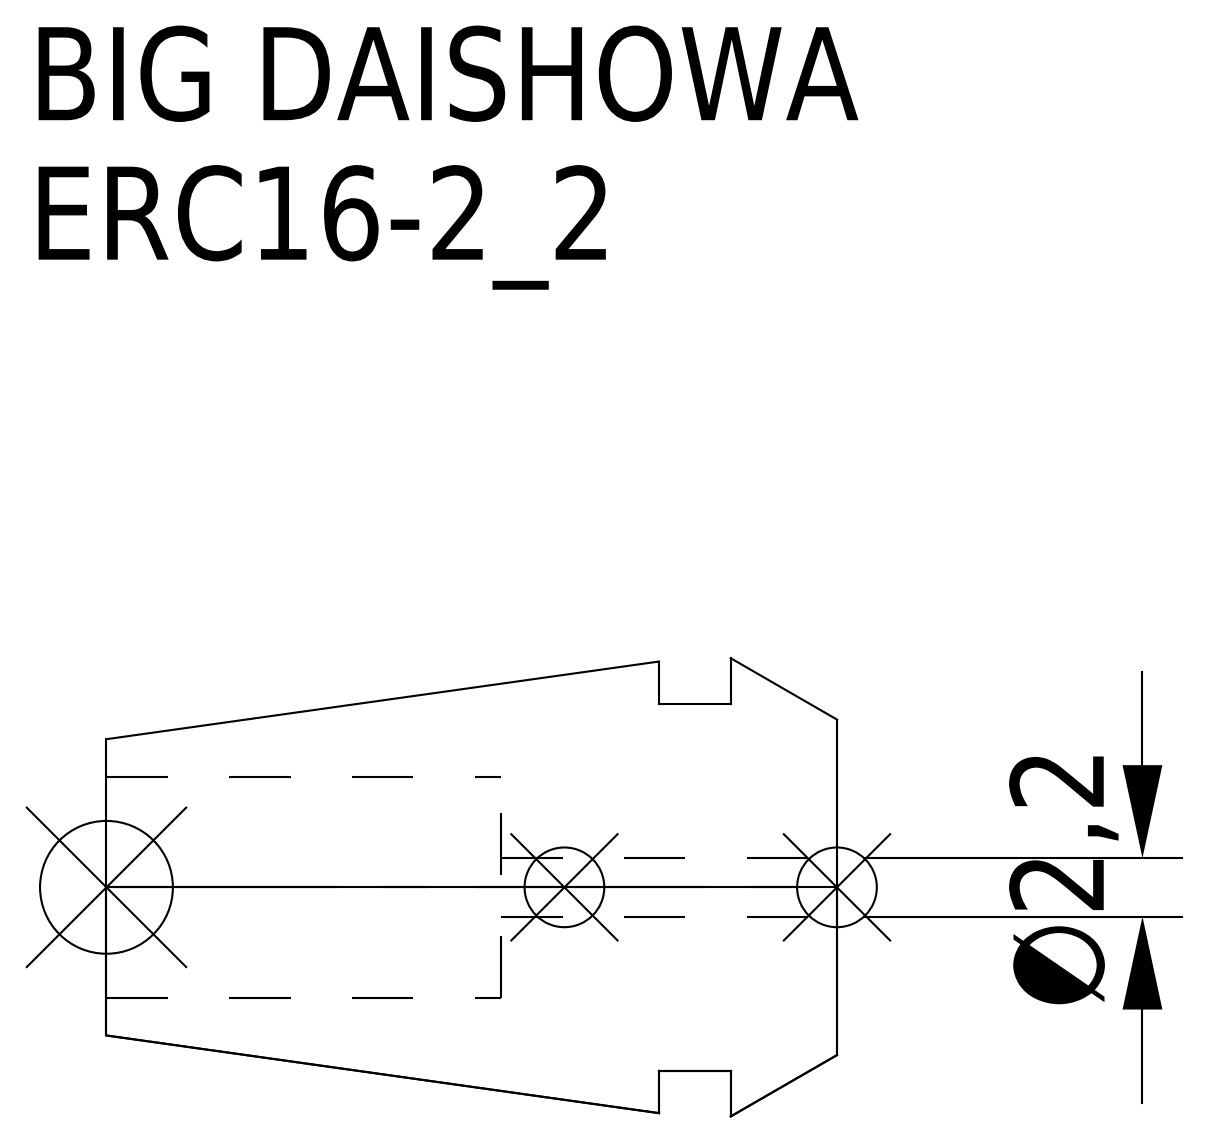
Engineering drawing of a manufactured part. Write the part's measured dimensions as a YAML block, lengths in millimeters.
part_name: "ERC16-2_2"
step_written_by: "CREO PARAMETRIC BY PTC INC, 2016380 (AUTOMOTIVE_DESIGN)"
units: millimeters
bodies: {solids: 1, faces: 15, planar: 5, cylindrical: 6, other: 4}
overall_size: [27.5, 17.25, 17.25]
volume: 3542
surface_area: 2115
round_holes:
  - {diameter: 2.2, count: 1}
  - {diameter: 8.3, count: 1}
round_bosses_or_shafts:
  - {diameter: 13.8, count: 1}
face_to_face_distances: [4, 6.7, 2.7, 12.63, 8.63, 5.93, 27.5, 23.5, 20.8, 14.87]
